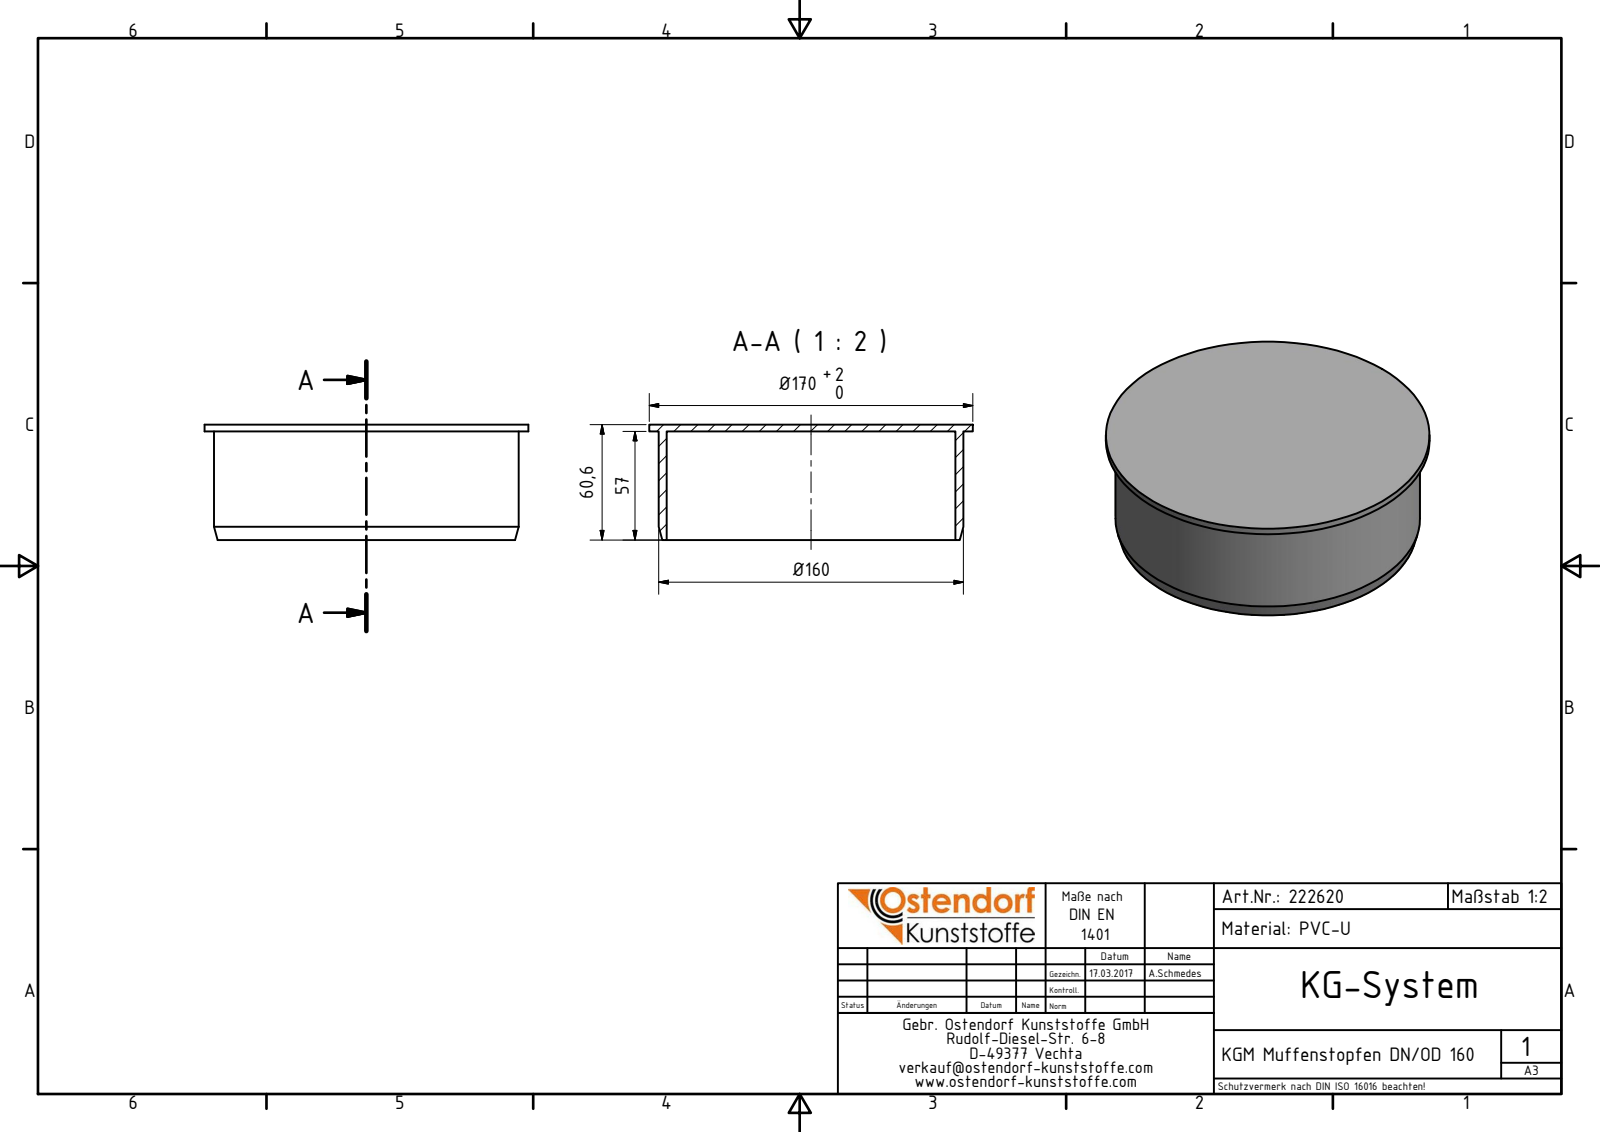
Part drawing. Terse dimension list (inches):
name: 222620 KGM Muffenstopfen DN_OD 160
written by: Autodesk Inventor 2016 (AUTOMOTIVE_DESIGN)
unit: in
bodies: 1 solid, 8 faces (4 planar, 3 cylindrical, 1 other)
size: 6.693 × 6.693 × 2.386
volume: 11.94 in³; area: 158.5 in²
holes: 1× ⌀5.969
bosses: 1× ⌀6.693, 1× ⌀6.299
face distances: 0.142, 2.244, 2.386
